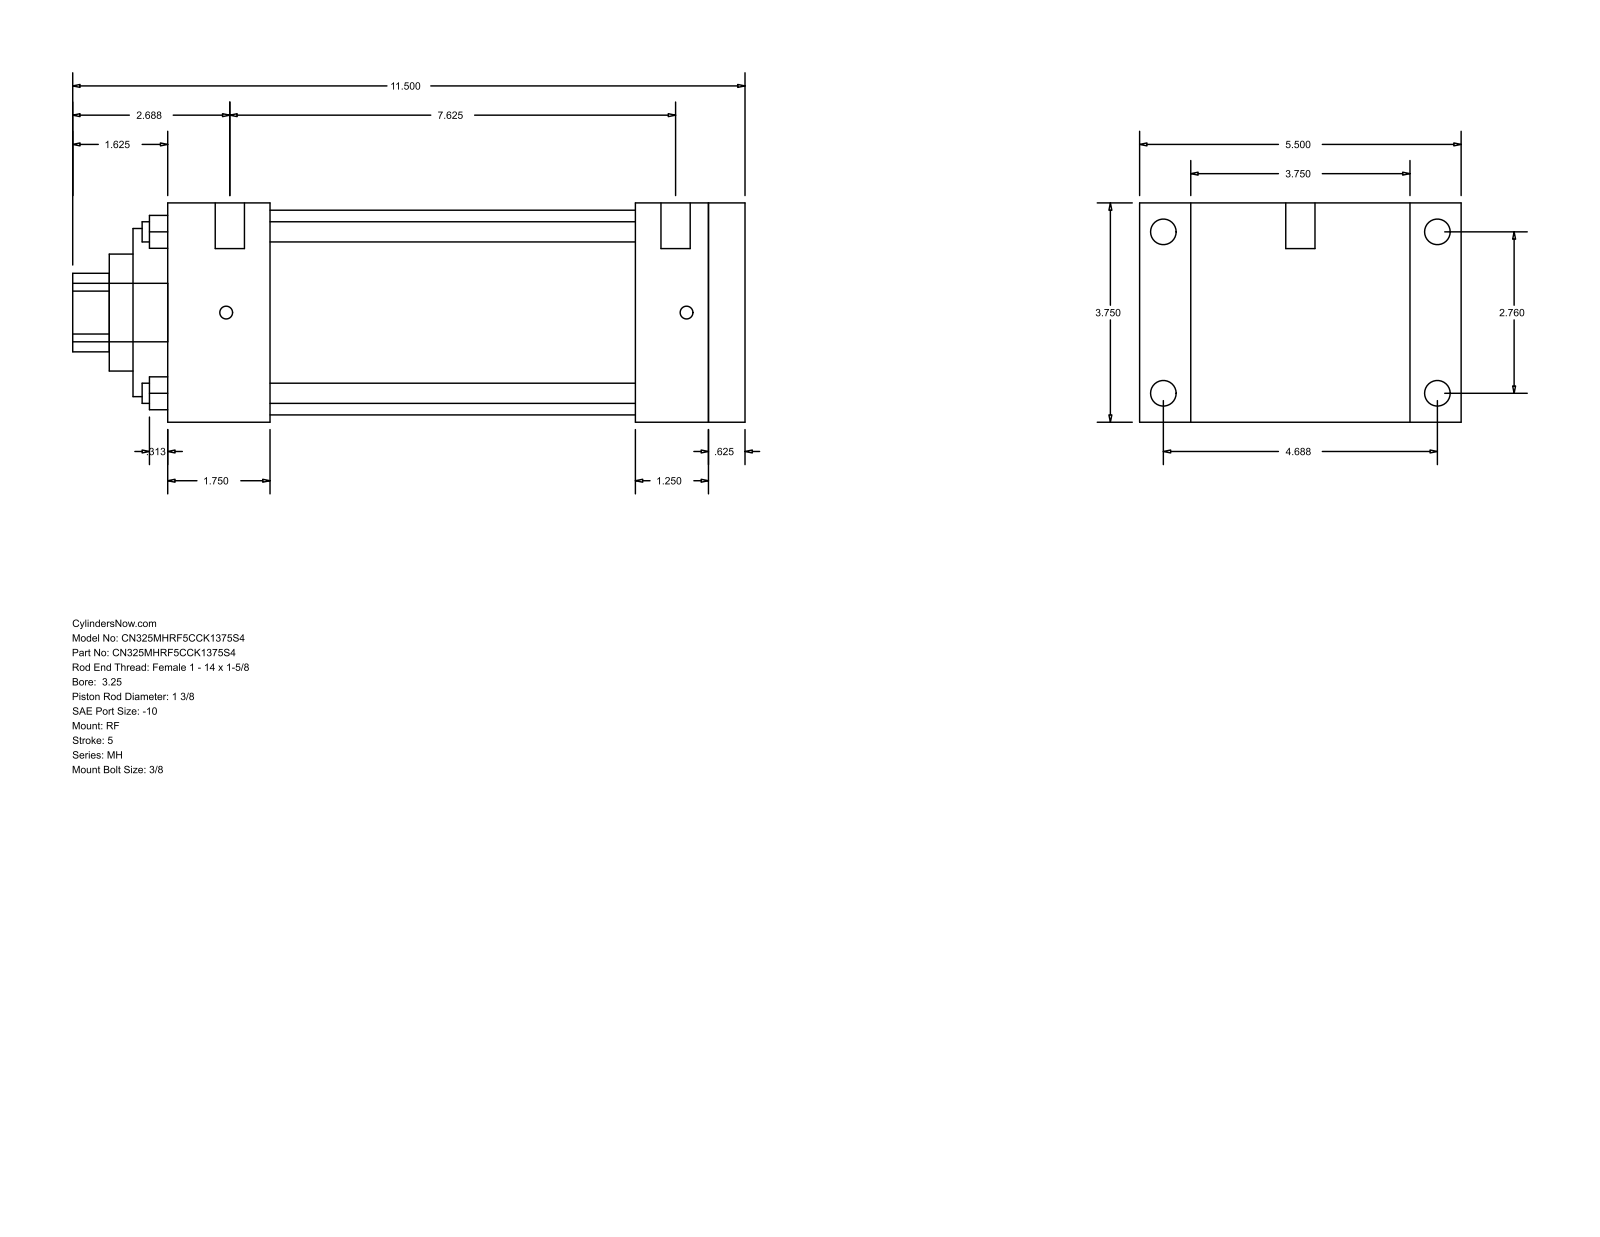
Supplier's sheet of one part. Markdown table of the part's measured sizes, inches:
| quantity | value |
| --- | --- |
| part name | MH_RF__0325_1.375 |
| STEP written by | GSSL Pune (CONFIG_CONTROL_DESIGN) |
| units | inches |
| bodies | 0 solids, 94 faces (65 planar, 29 cylindrical, 0 other) |
| overall size | 11.5 × 5.5 × 3.75 |
| round holes (diameter × count) | 0.345 × 4, 1.375 × 1, 2 × 1, 2.875 × 1, 3.5 × 1 |
| round bosses / shafts (diameter × count) | 0.438 × 4, 0.219 × 4, 0.5 × 2, 1 × 1 |
| partial cylindrical surfaces (radius × count) | 0.672 × 1 |
| main face-to-face distances | 3.75, 9.875, 9.25, 0.625, 0.875, 4.625, 1.75, 7.5, 8.125, 8 |
| hole center spacings | 1.952, 2.76, 3.903 |
